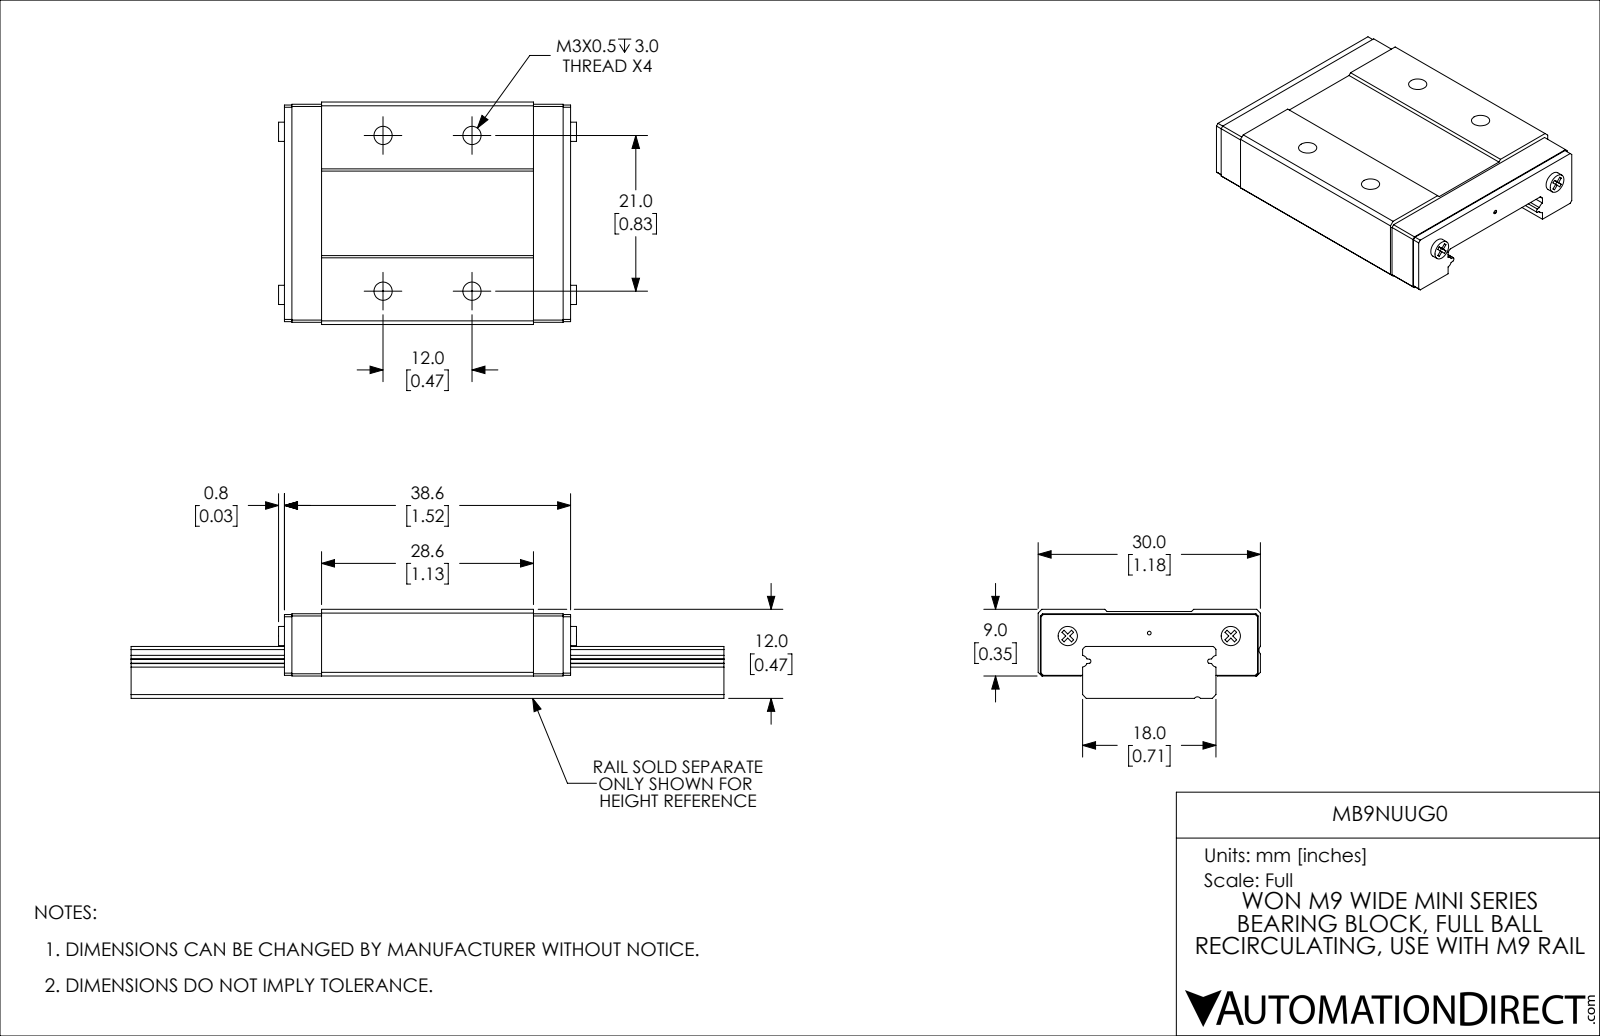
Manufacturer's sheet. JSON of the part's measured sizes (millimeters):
{"part_name": "MB9NUUG0", "step_written_by": "SolidWorks 2019 (CONFIG_CONTROL_DESIGN)", "units": "millimeters", "bodies": {"solids": 1, "faces": 156, "planar": 119, "cylindrical": 29, "other": 8}, "overall_size": [40.2, 30, 9], "volume_mm3": 7315, "surface_area_mm2": 3891, "round_holes": [[2.46, 4], [0.5, 1]], "round_bosses_or_shafts": [[2.6, 2]], "partial_cylinders_radius": [[0.8, 3], [0.32, 2], [0.95, 2]], "face_to_face_distances": [5, 4, 9, 8.7, 4.7, 8.4, 4.4, 0.6, 30, 38.6], "hole_center_spacings": [12, 21, 24.19]}
